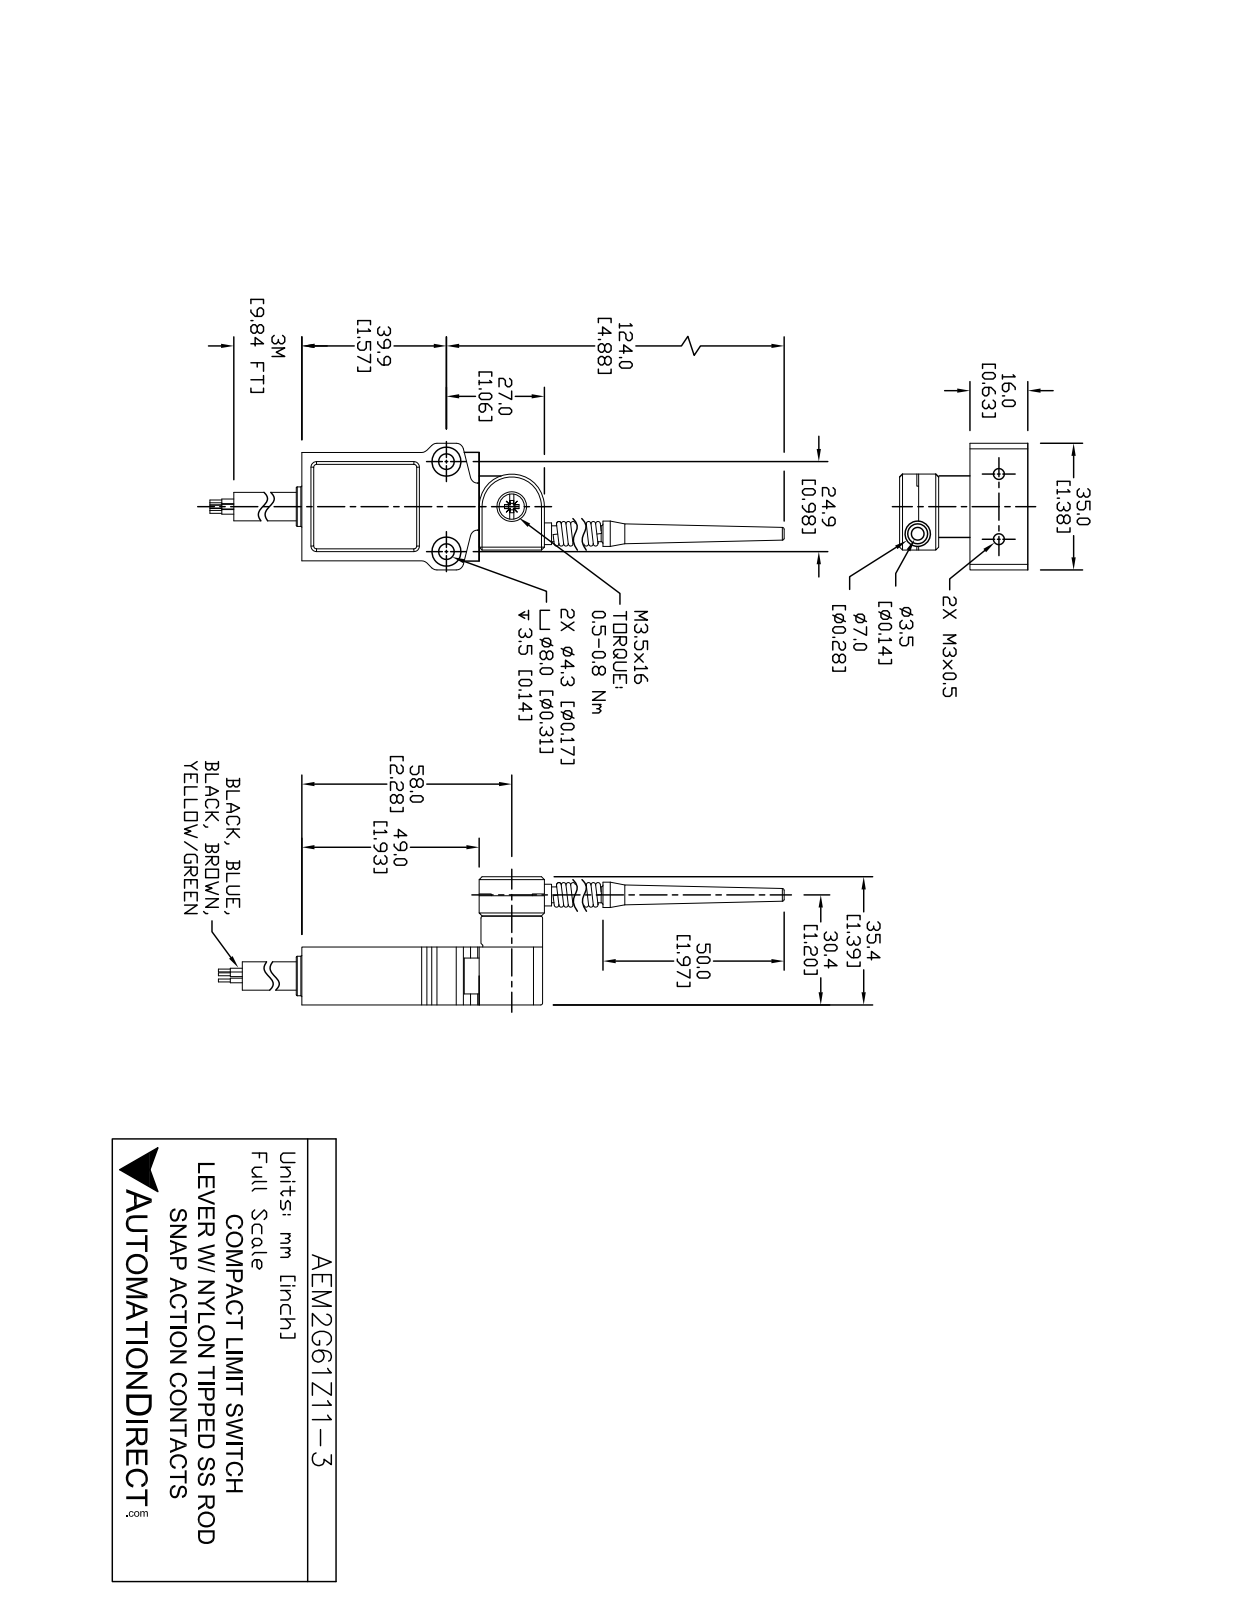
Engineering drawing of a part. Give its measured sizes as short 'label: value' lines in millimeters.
name: AEM2G61Z11-3_Default
written by: SolidWorks 2021 (CONFIG_CONTROL_DESIGN)
unit: mm
bodies: 4 solids, 199 faces (99 planar, 83 cylindrical, 17 other)
size: 176.7 × 38 × 35
volume: 33 580 mm³; area: 14 280 mm²
holes: 2× ⌀3, 2× ⌀4.4, 2× ⌀8.2, 1× ⌀5, 1× ⌀8.1
bosses: 2× ⌀7, 1× ⌀15.8, 1× ⌀6.1, 1× ⌀3.6, 1× ⌀3.6
rounds: 8× R2, 1× R6.5, 1× R9
face distances: 16, 30, 5.5, 9, 49, 25, 14.5, 30.5, 5.3, 14.3
hole spacings: 21.9, 19, 25
